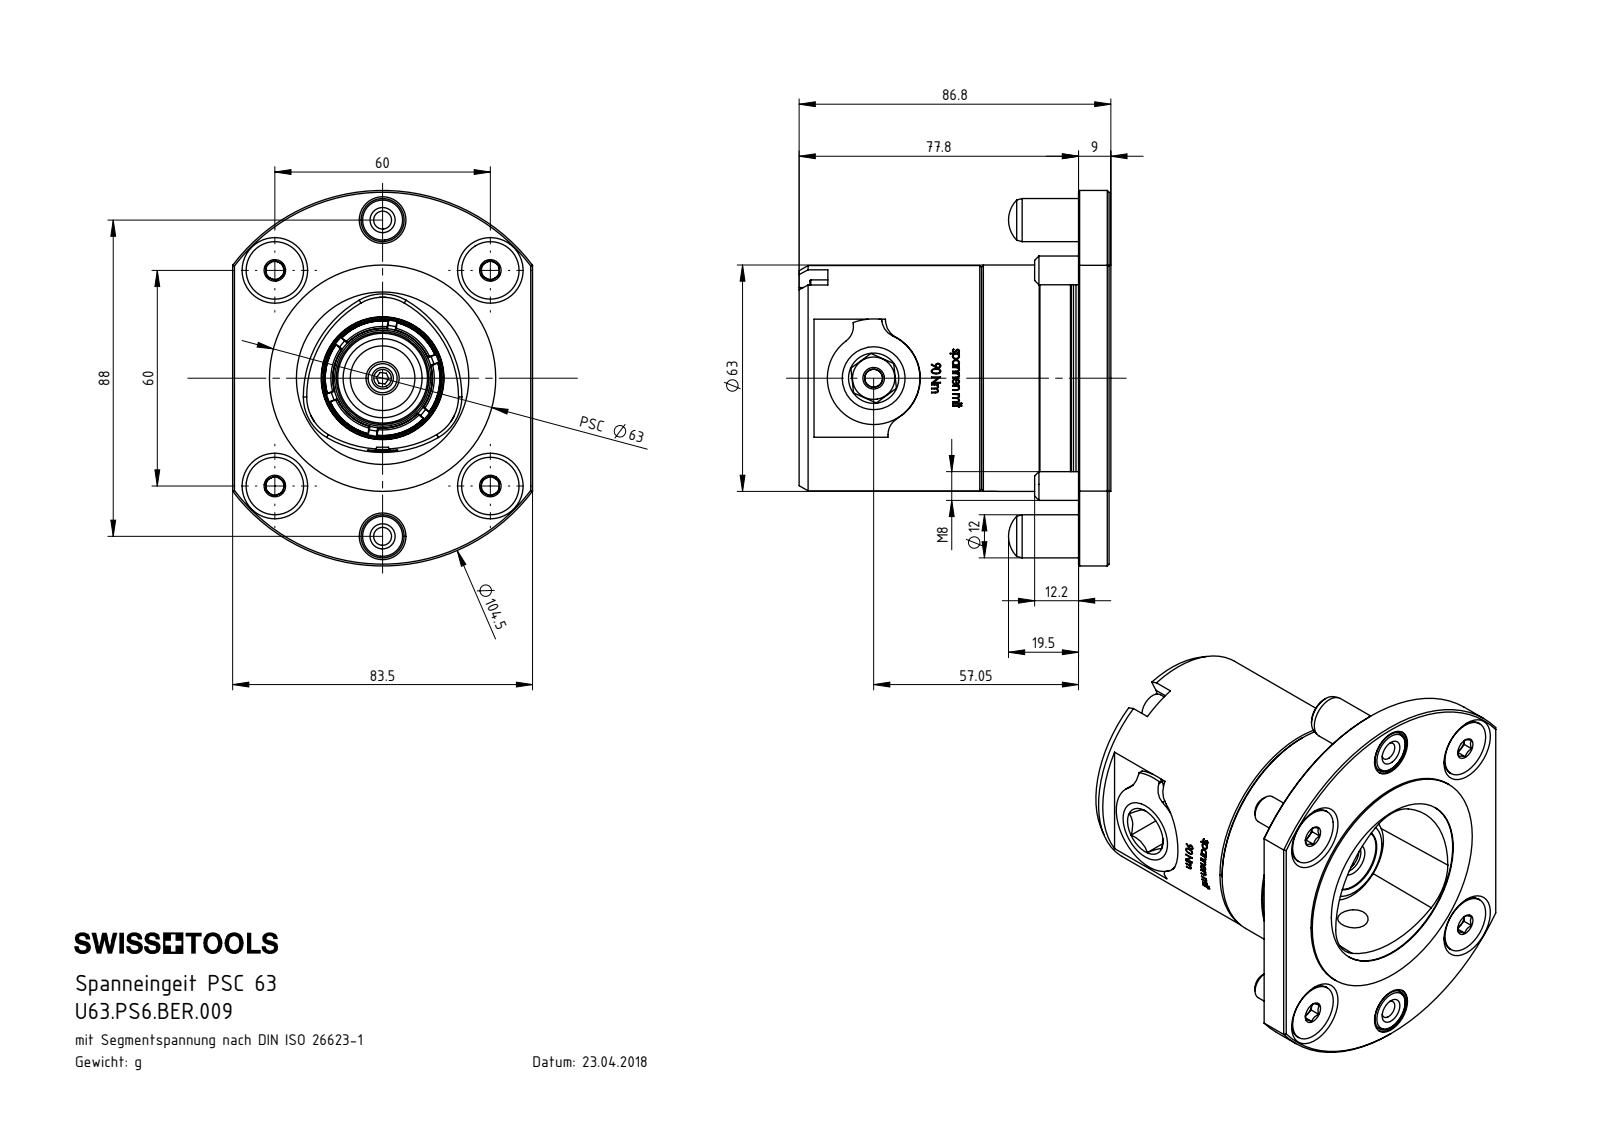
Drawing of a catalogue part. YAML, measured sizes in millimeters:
part_name: "O-Ring_1.50-AD18.00; DIN 3771 - 19x2; 986.19337.000.1; ISO 4762 - M5 x 50 (+8 more)"
step_written_by: "SolidWorks 2017 (AUTOMOTIVE_DESIGN)"
units: millimeters
bodies: {solids: 29, faces: 916, planar: 253, cylindrical: 268, other: 395}
overall_size: [104.5, 86.8, 83.75]
volume: 249008
surface_area: 93469
round_holes:
  - {diameter: 5, count: 4}
  - {diameter: 8.2, count: 4}
  - {diameter: 2.1, count: 2}
  - {diameter: 3, count: 2}
  - {diameter: 4.2, count: 2}
  - {diameter: 4.97, count: 2}
  - {diameter: 5.5, count: 2}
  - {diameter: 12, count: 2}
  - {diameter: 13, count: 2}
  - {diameter: 2.4, count: 1}
  - {diameter: 4, count: 1}
  - {diameter: 8.1, count: 1}
round_bosses_or_shafts:
  - {diameter: 16, count: 4}
  - {diameter: 8, count: 4}
  - {diameter: 8.5, count: 2}
  - {diameter: 5, count: 2}
  - {diameter: 63, count: 1}
  - {diameter: 62.7, count: 1}
  - {diameter: 59, count: 1}
  - {diameter: 55, count: 1}
partial_cylinders:
  - {radius: 6, count: 4}
  - {radius: 5, count: 2}
  - {radius: 5.1, count: 2}
  - {radius: 5.2, count: 2}
  - {radius: 7.5, count: 1}
  - {radius: 11.75, count: 1}
  - {radius: 13, count: 1}
  - {radius: 14, count: 1}
face_to_face_distances: [8.5, 31.2, 39.7, 46.6, 77.8, 86.3, 49.4, 2.8, 28.4, 36.9]
hole_center_spacings: [33.11, 42.43, 60, 79.85, 15, 20.42, 23.51, 25.5]
